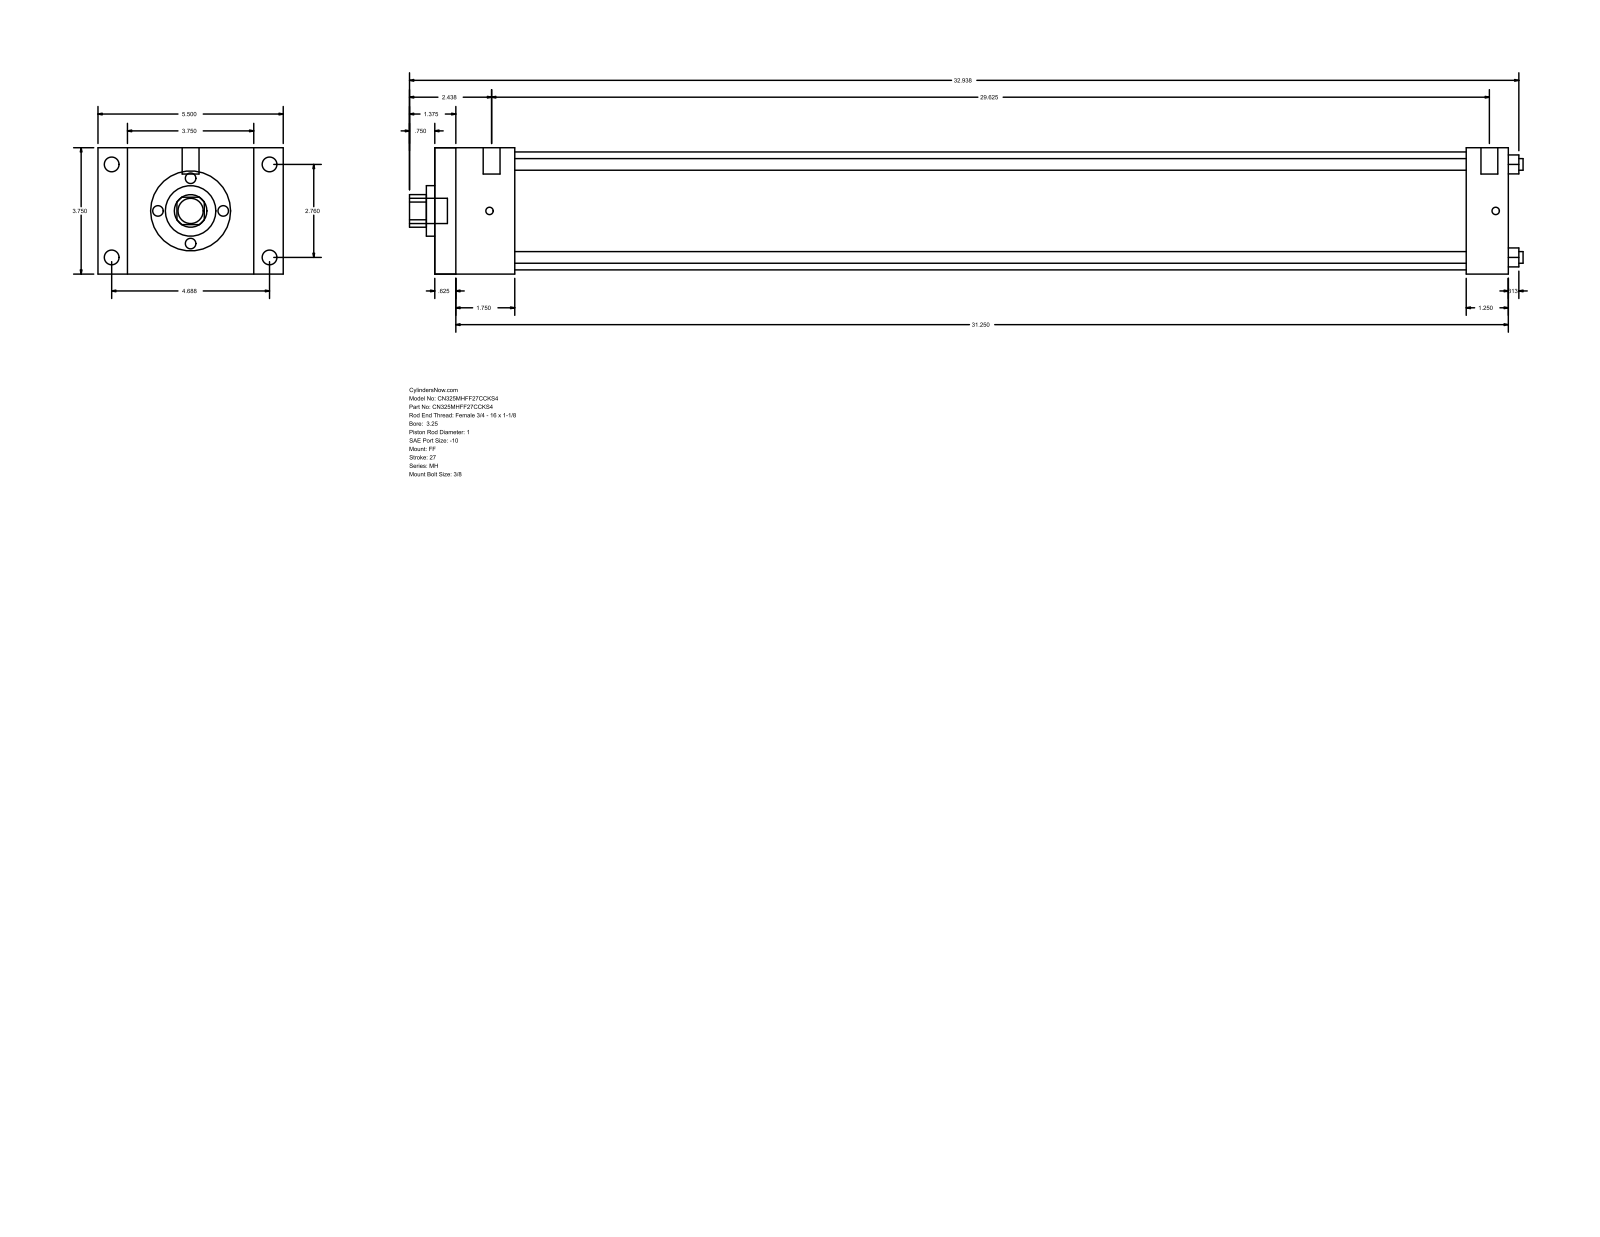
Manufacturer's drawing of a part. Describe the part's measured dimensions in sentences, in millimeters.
The part is named "MH_FF__0325_1". Its 3-D file was written by "GSSL Pune (CONFIG_CONTROL_DESIGN)". It is 0 solids with 92 faces: 64 planar, 28 cylindrical and 0 other. Overall it measures 839.79 by 139.7 by 95.25 millimeters. Round holes: 4 of diameter 8.76, 1 of diameter 25.4, 1 of diameter 38.1, 1 of diameter 88.9. Round bosses or shafts: 4 of diameter 11.13, 4 of diameter 5.56, 2 of diameter 12.7, 1 of diameter 19.05. Partial cylindrical surfaces (rounded edges, fillets, slot ends): 1 of radius 12.29. The main face-to-face distances are 95.24, 809.62, 15.87, 793.75, 22.23, 117.47, 777.87, 762, 31.75, 60.33. The hole center spacings are 49.57, 70.1, 99.14.
